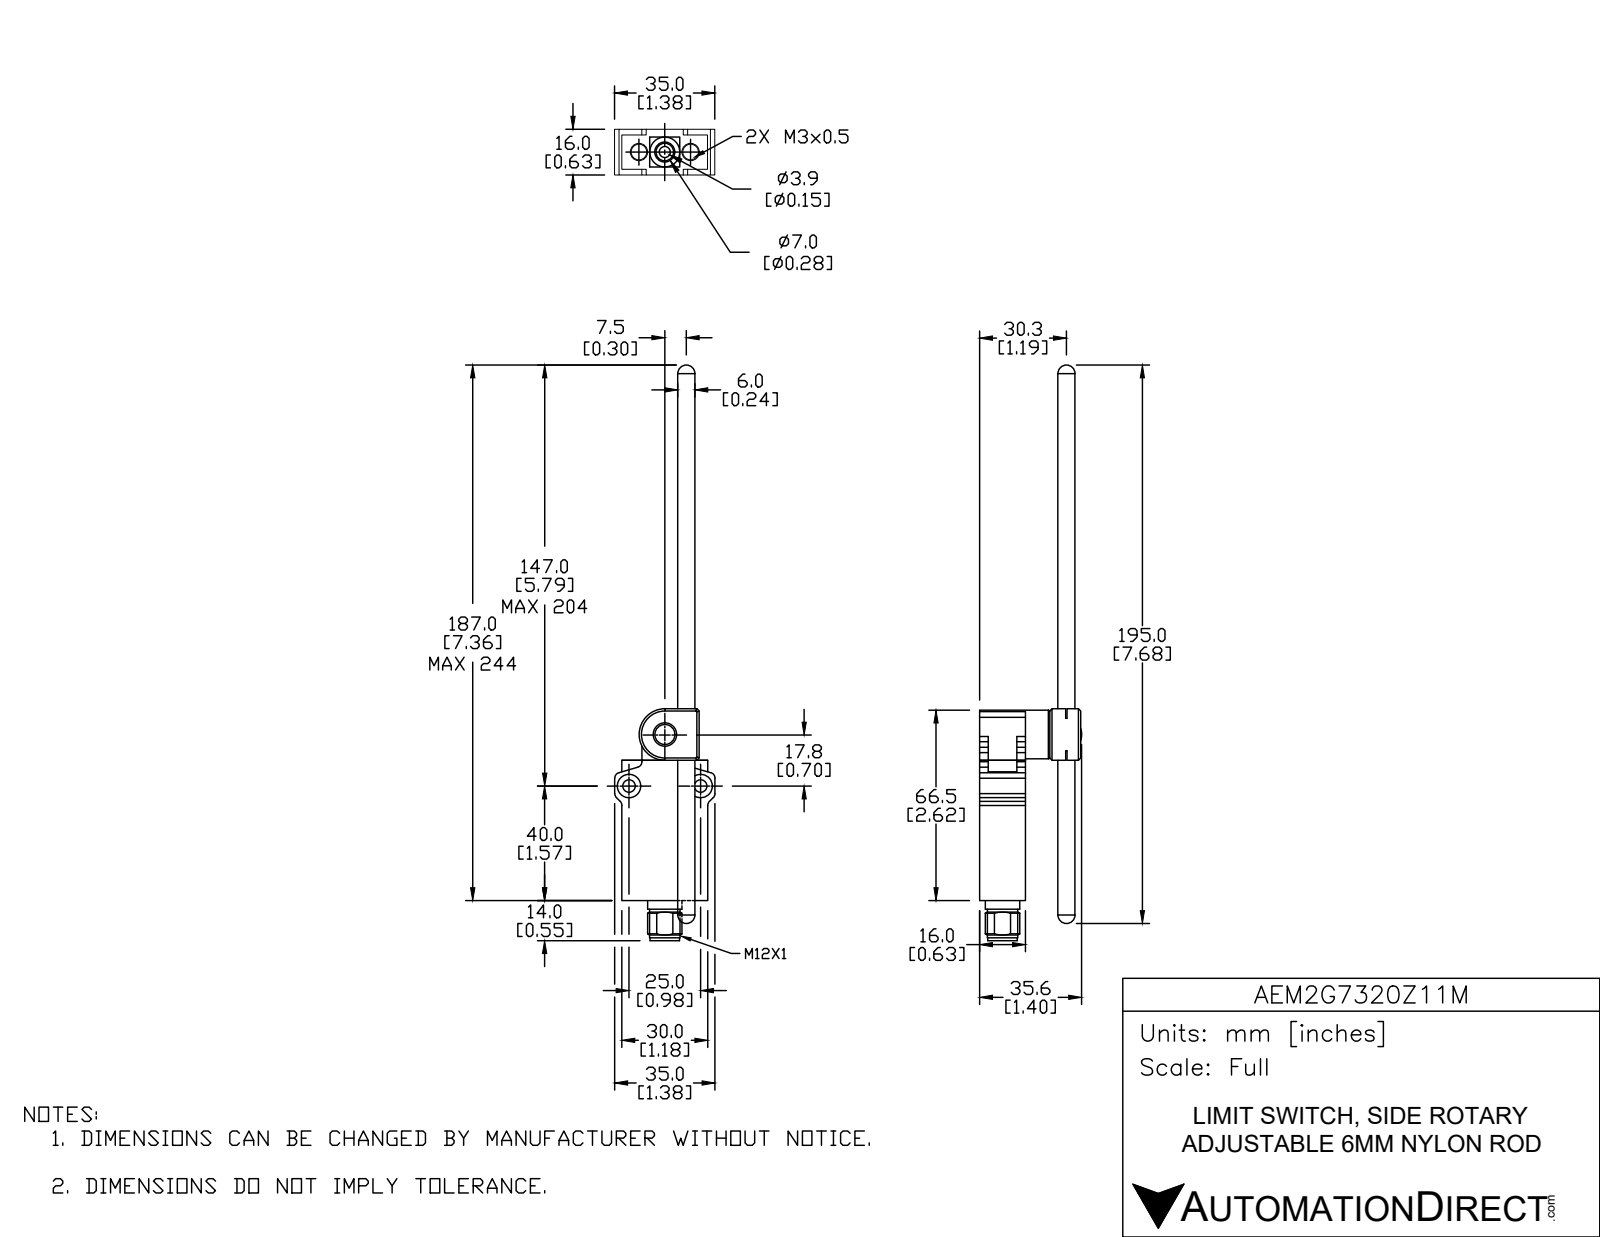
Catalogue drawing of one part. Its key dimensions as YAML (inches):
part_name: "AEM2G7320Z11M_a"
step_written_by: "SolidWorks 2018 (AUTOMOTIVE_DESIGN)"
units: inches
bodies: {solids: 6, faces: 186, planar: 96, cylindrical: 53, other: 37}
overall_size: [8.05, 1.378, 1.374]
volume: 2.353
surface_area: 23.91
round_holes:
  - {diameter: 0.118, count: 2}
  - {diameter: 0.173, count: 2}
  - {diameter: 0.323, count: 2}
  - {diameter: 0.197, count: 1}
  - {diameter: 0.236, count: 1}
  - {diameter: 0.315, count: 1}
round_bosses_or_shafts:
  - {diameter: 0.622, count: 1}
  - {diameter: 0.472, count: 1}
  - {diameter: 0.417, count: 1}
  - {diameter: 0.406, count: 1}
  - {diameter: 0.276, count: 1}
  - {diameter: 0.118, count: 1}
partial_cylinders:
  - {radius: 0.079, count: 8}
  - {radius: 0.256, count: 1}
  - {radius: 0.354, count: 1}
face_to_face_distances: [0.63, 1.181, 0.177, 0.354, 0.535, 1.165, 0.358, 0.28, 0.902, 0.098]
hole_center_spacings: [0.866, 0.748, 0.857, 0.984, 1.065]
